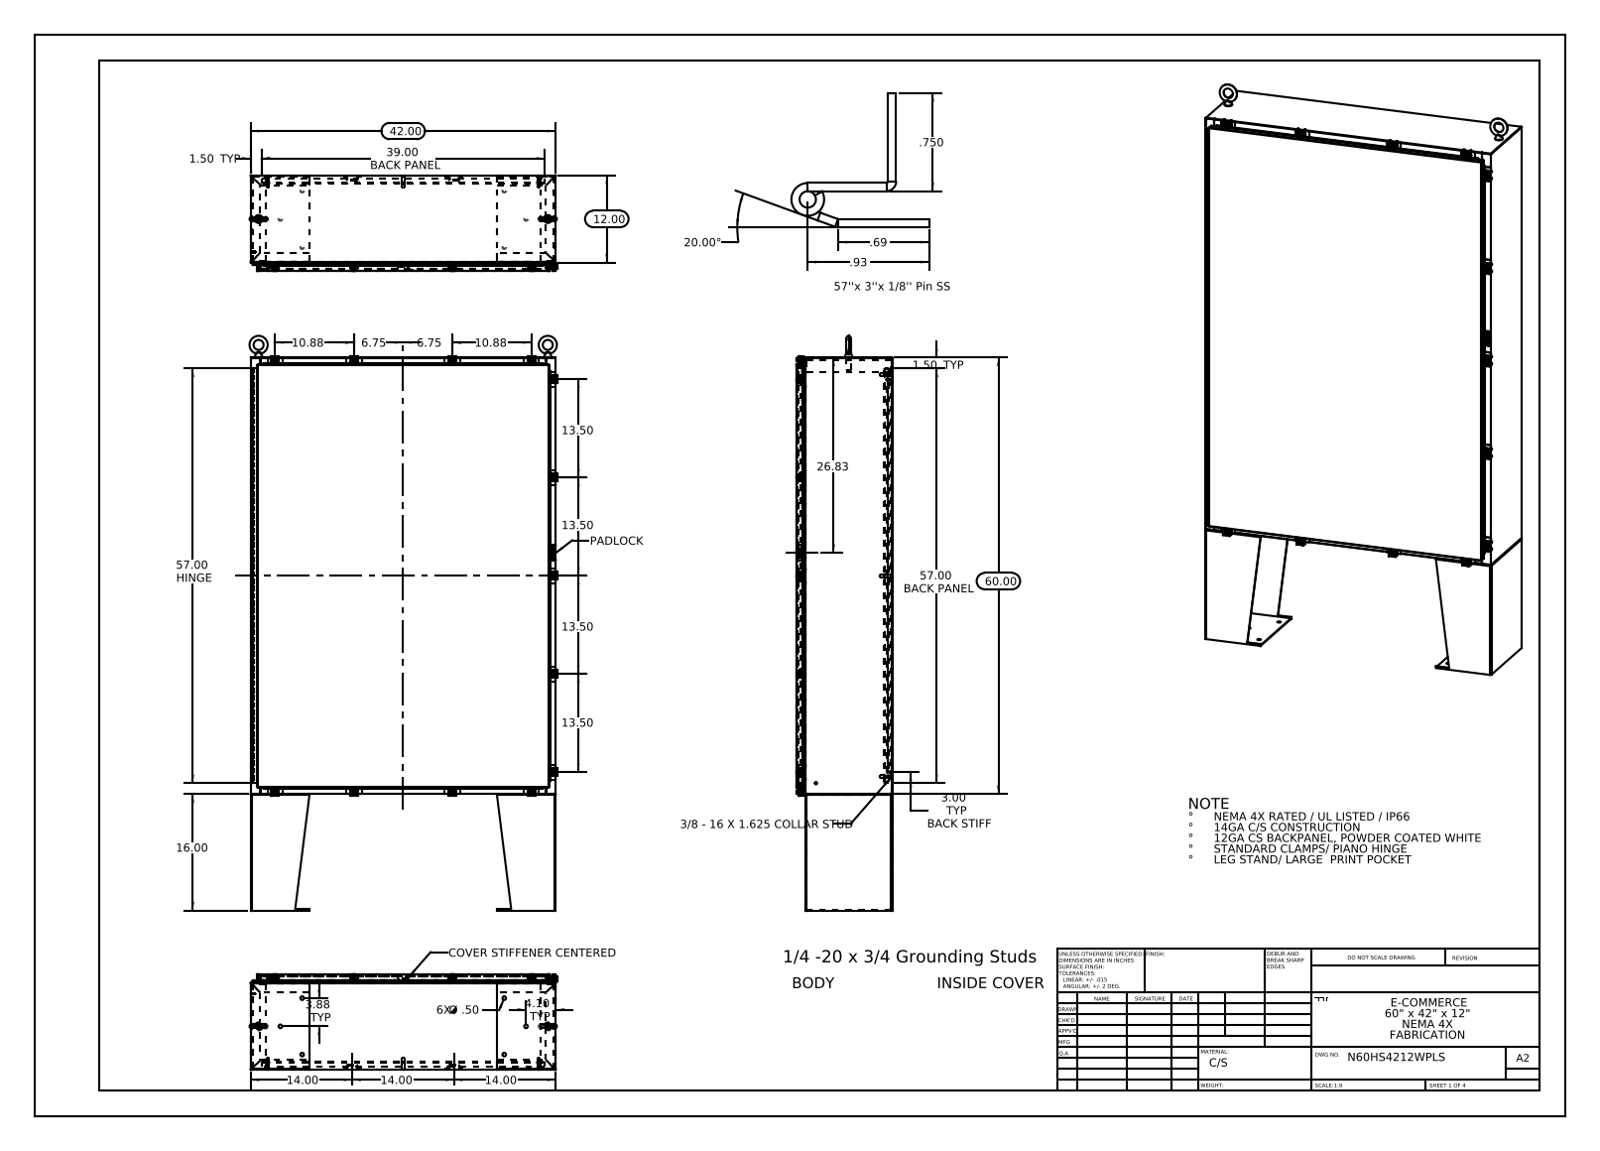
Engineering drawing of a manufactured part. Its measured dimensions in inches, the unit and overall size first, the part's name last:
Units: inches
Overall size (bounding box): 79 × 42.346 × 13.201
Round holes (diameter × count): ⌀0.5 ×14, ⌀0.213 ×13, ⌀0.26 ×13, ⌀0.25 ×8, ⌀0.75 ×4, ⌀0.125 ×2, ⌀0.125 ×1
Round bosses / shafts (diameter × count): ⌀0.25 ×14, ⌀0.5 ×13, ⌀0.399 ×13, ⌀0.625 ×10, ⌀0.375 ×8, ⌀0.33 ×8, ⌀0.157 ×8, ⌀0.14 ×8
Partial cylindrical surfaces — rounded edges, fillets, slot ends (radius × count): R0.06 ×58, R0.013 ×39, R0.088 ×33, R0.12 ×26, R0.141 ×26, R0.05 ×23, R0.145 ×22, R0.08 ×18
Main face-to-face distances: 0.075, 13.126, 0.104, 13.051, 1.075, 13.201, 1, 12.126, 12.051, 1.179
Hole centre spacings: 13.5, 2.225, 7.069, 7.137, 27.625, 29.743, 31.035, 32.01
Volume: 1 026 in³ · Surface area: 24 722 in²
Bodies: 103 solids, 3908 faces (1992 planar, 1616 cylindrical, 300 other)
Part name (STEP PRODUCT): Eye-Bolt_Stiffener WMT Template 1901; N60HS4212SSWPLS 22104005_DEFAULT; Quarter-20 CD Stud; N60HS4212SSWPLS SD-LSK - Base (+8 more)
STEP written by: SolidWorks 2013 (CONFIG_CONTROL_DESIGN)
